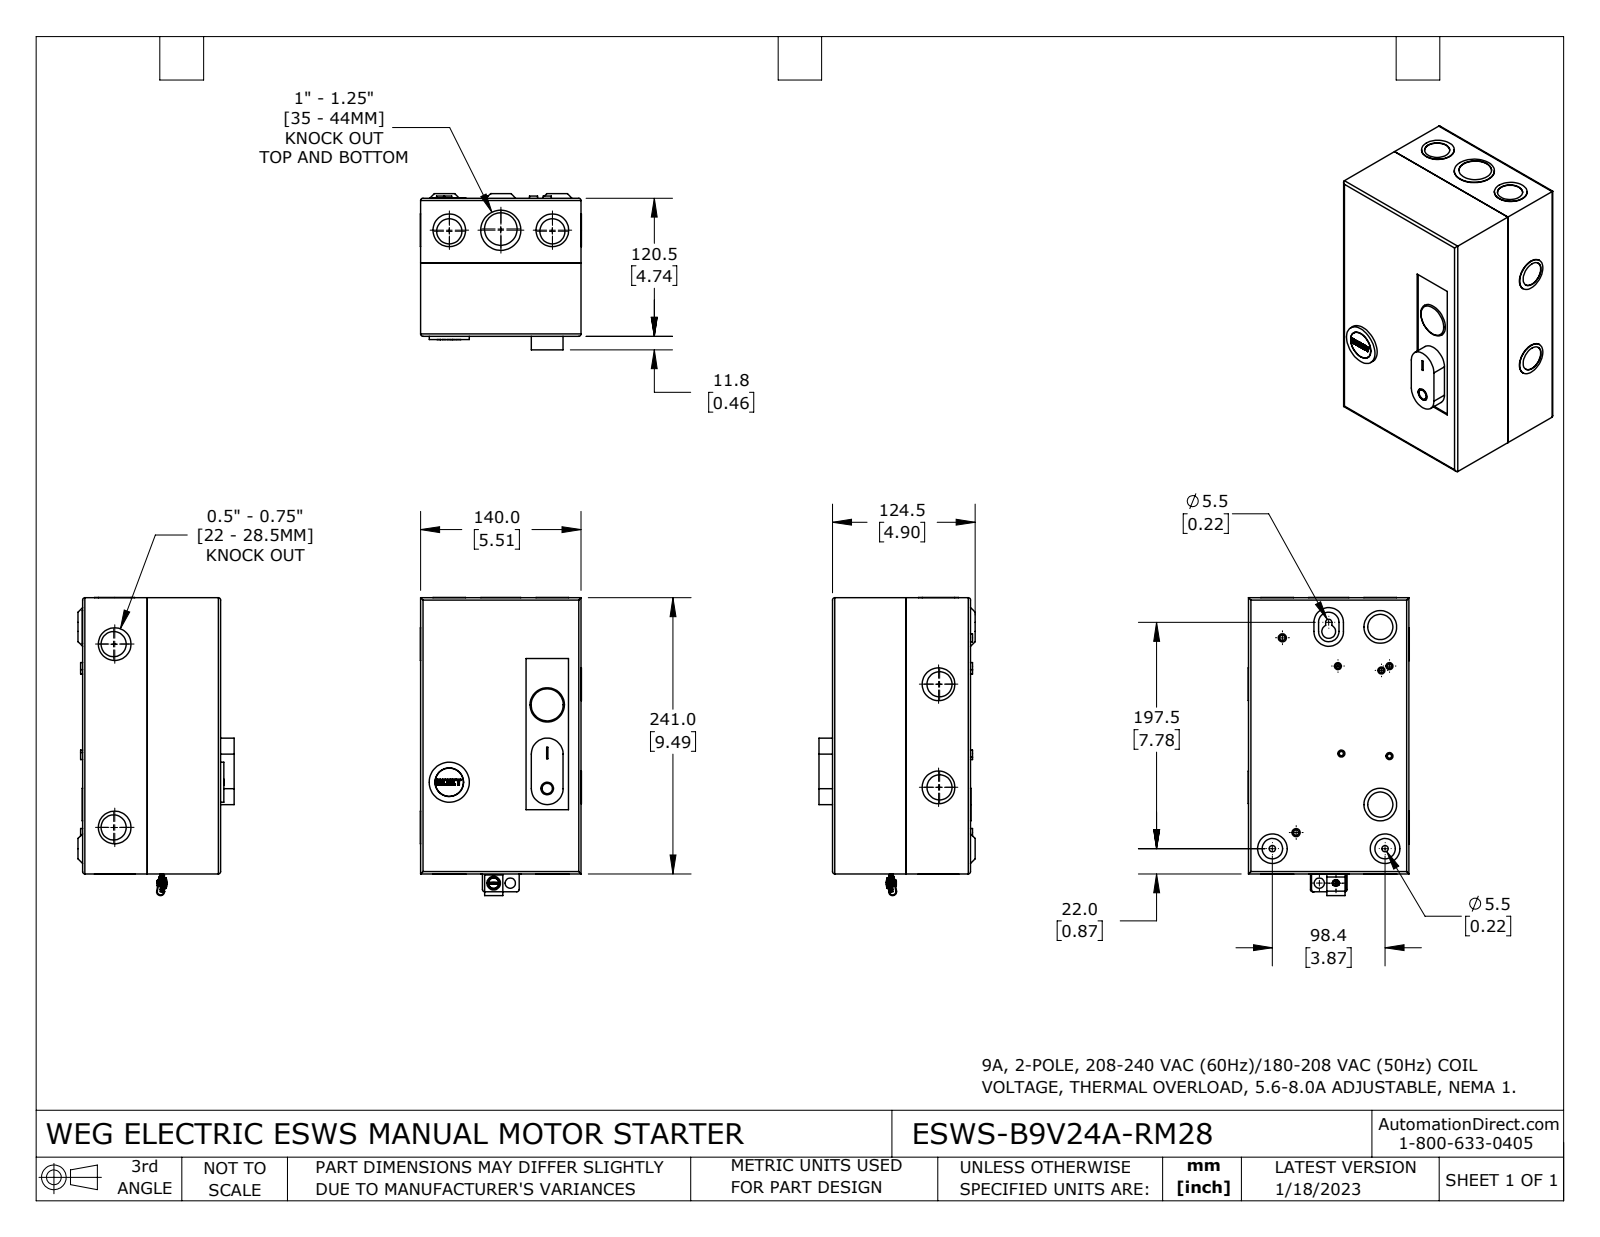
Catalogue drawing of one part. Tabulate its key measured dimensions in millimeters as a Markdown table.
| quantity | value |
| --- | --- |
| part name | ESWS-B9V24A-RM28 |
| STEP written by | SolidWorks 2021 (CONFIG_CONTROL_DESIGN) |
| units | millimeters |
| bodies | 7 solids, 435 faces (168 planar, 230 cylindrical, 37 other) |
| overall size | 260.3 × 140.6 × 136.3 |
| volume | 266 000 mm³ |
| surface area | 377 500 mm² |
| round holes (diameter × count) | 3.7 × 5, 21.9 × 4, 4.6 × 2, 5.5 × 2, 9 × 2, 21.9 × 2, 22 × 2, 22.5 × 2, 6.5 × 1, 7.7 × 1, 11 × 1, 11.9 × 1 |
| round bosses / shafts (diameter × count) | 28.5 × 6, 6.1 × 5, 28.5 × 2, 7.1 × 2, 35.1 × 1, 35 × 1, 30.3 × 1, 29.2 × 1 |
| partial cylindrical surfaces (radius × count) | 0.1 × 34, 2 × 13, 0.8 × 4, 2.7 × 3, 1.5 × 2, 1.9 × 2, 3.1 × 2, 3.5 × 2 |
| main face-to-face distances | 1.2, 119.3, 138.8, 118.1, 239.8, 120.5, 137.6, 140, 1.8, 1.6 |
| hole center spacings | 14.5, 35, 45, 86, 90, 125, 152.3, 190.1 |
